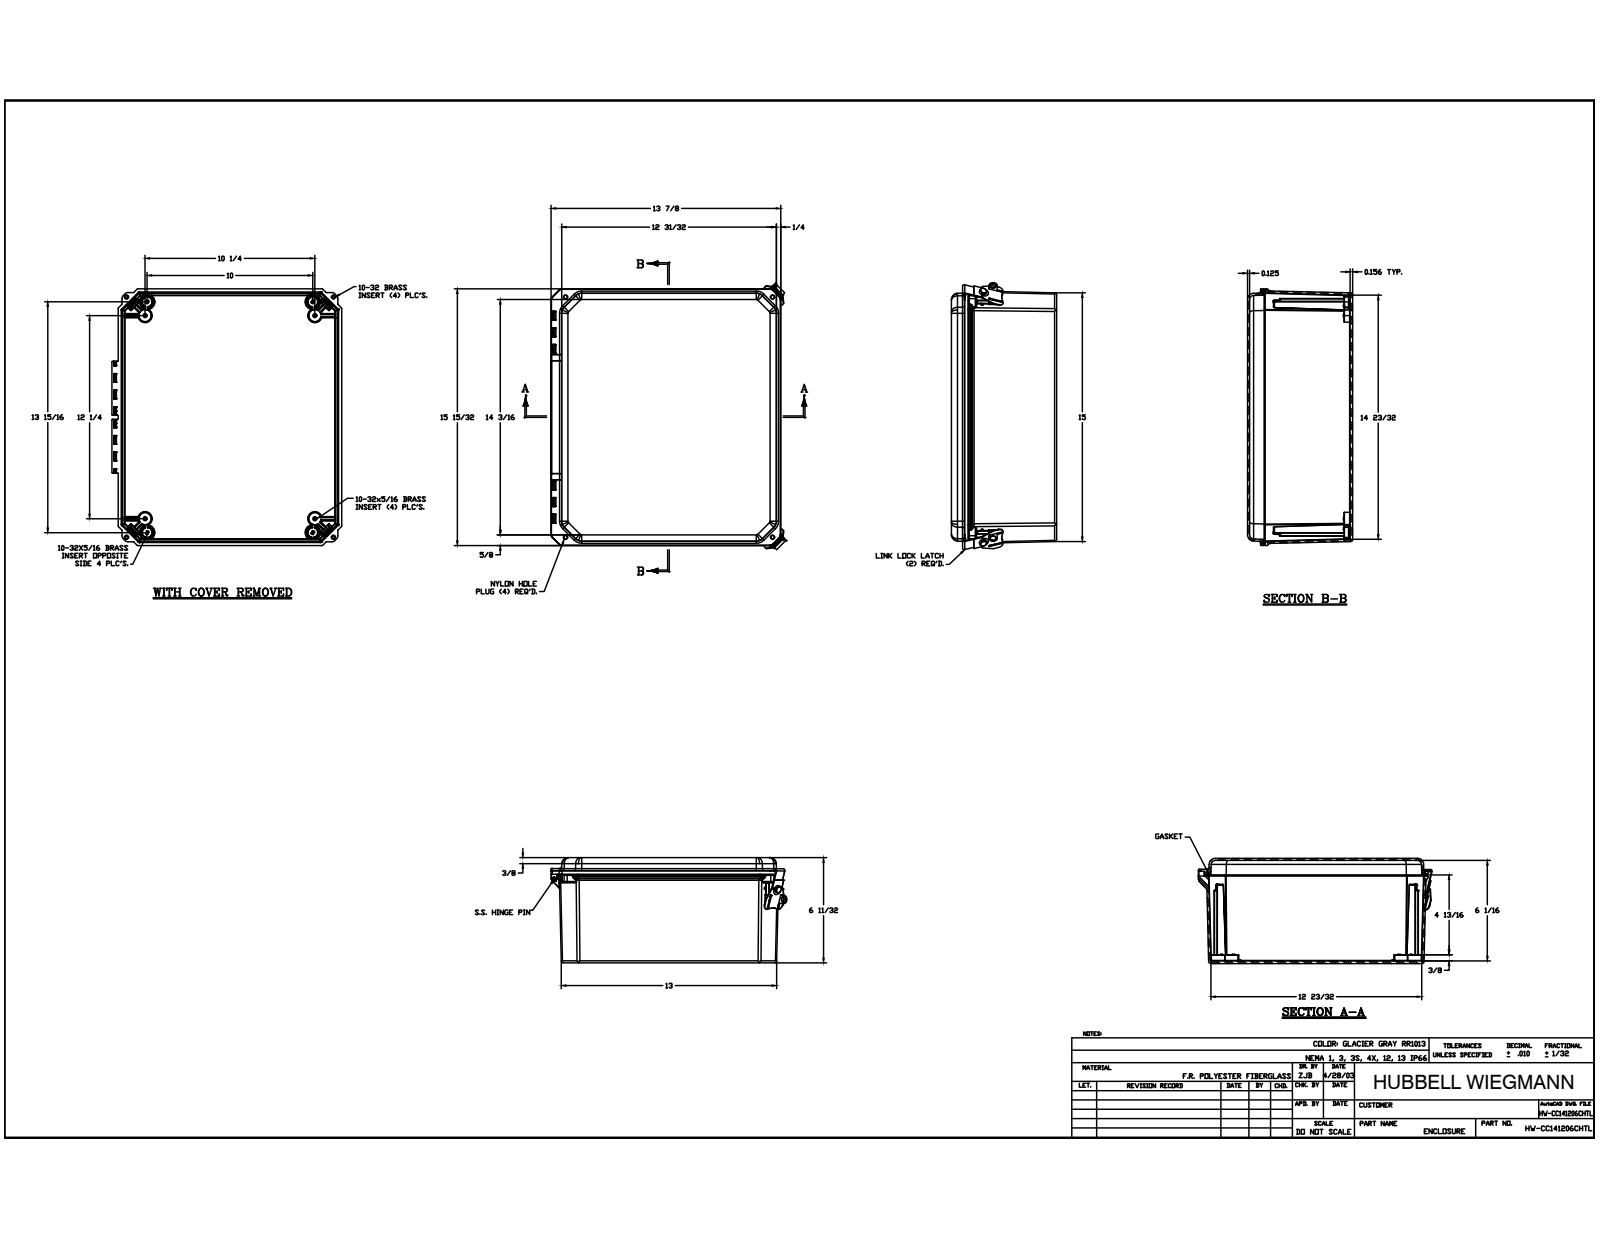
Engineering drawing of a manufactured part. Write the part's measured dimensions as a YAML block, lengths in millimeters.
part_name: "DS141206BOX; DSCC141206CVR; GA141206; WP1412HLU (+5 more)"
step_written_by: "Autodesk Inventor 2014 (AUTOMOTIVE_DESIGN)"
units: millimeters
bodies: {solids: 31, faces: 2387, planar: 696, cylindrical: 940, other: 751}
overall_size: [415.24, 363.11, 161.11]
volume: 1834000
surface_area: 1034000
round_holes:
  - {diameter: 3.96, count: 12}
  - {diameter: 3.86, count: 8}
  - {diameter: 2.49, count: 4}
  - {diameter: 3.81, count: 4}
  - {diameter: 5.56, count: 4}
  - {diameter: 6.4, count: 4}
  - {diameter: 7.92, count: 4}
  - {diameter: 1.27, count: 2}
  - {diameter: 3.05, count: 2}
  - {diameter: 9.22, count: 2}
  - {diameter: 3.48, count: 1}
round_bosses_or_shafts:
  - {diameter: 6.25, count: 12}
  - {diameter: 22.1, count: 4}
  - {diameter: 5.3, count: 4}
  - {diameter: 5.08, count: 4}
  - {diameter: 3.43, count: 3}
  - {diameter: 15.24, count: 2}
  - {diameter: 1.27, count: 2}
partial_cylinders:
  - {radius: 0.25, count: 225}
  - {radius: 0.13, count: 116}
  - {radius: 0.51, count: 59}
  - {radius: 3.17, count: 41}
  - {radius: 0.76, count: 37}
  - {radius: 0.99, count: 28}
  - {radius: 6.35, count: 26}
  - {radius: 0.76, count: 24}
face_to_face_distances: [3.17, 3.96, 161.11, 157.15, 157.94, 153.98, 3.55, 3.53, 23.8, 134.14]
hole_center_spacings: [368, 340.76, 362.06, 10.9, 20.15, 21.35, 32.44, 40.18]
